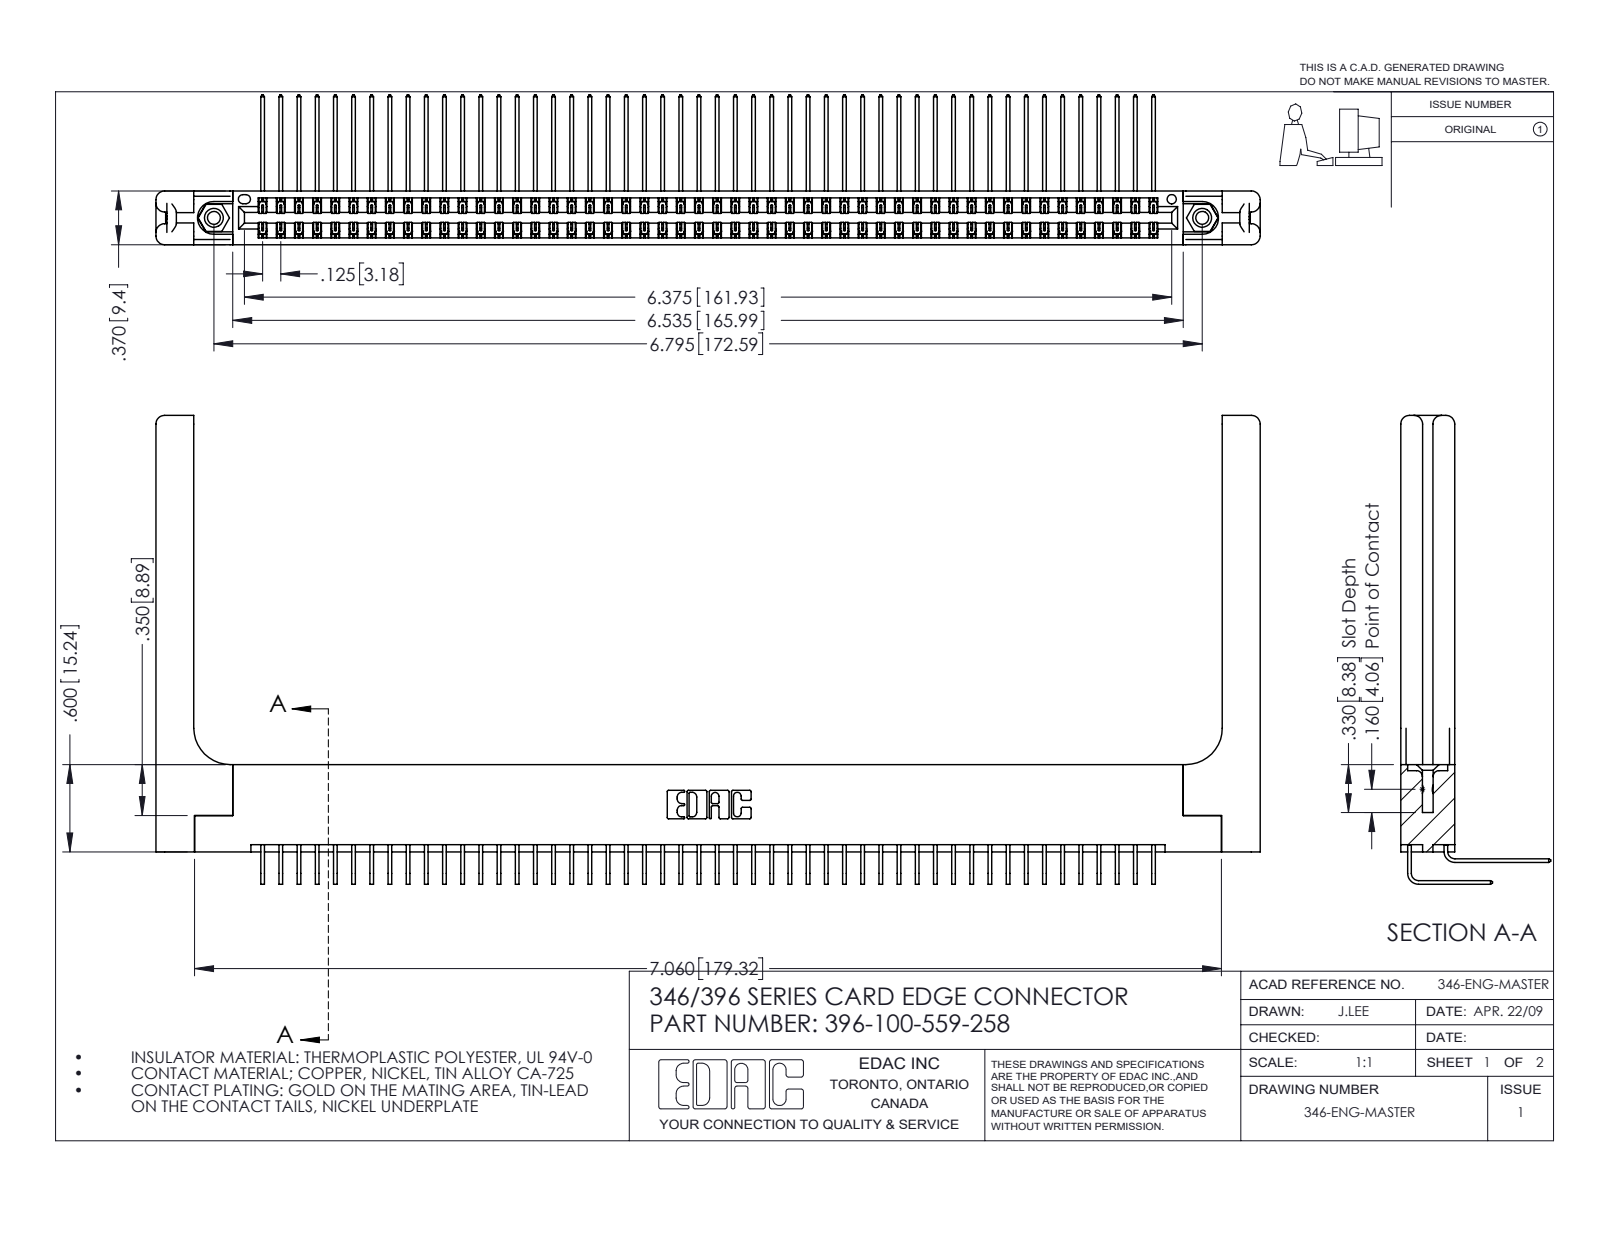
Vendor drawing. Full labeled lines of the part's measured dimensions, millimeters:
Part name (STEP PRODUCT): 345-292-001_558 559 Tail - 1; 345-250-001_345-250-001-102; 346 Part_Flush Mounting Lugs - 0.156 Dia-TH; 346-220-058_345-220-058 (+2 more)
STEP written by: SolidWorks 2016 (CONFIG_CONTROL_DESIGN)
Units: millimetres
Bodies: 105 solids, 5778 faces (3924 planar, 1794 cylindrical, 60 other)
Overall size (bounding box): 192.8 × 81.9 × 26.2
Volume: 26 940 mm³ · Surface area: 34 590 mm²
Round holes (diameter × count): ⌀2.3 ×2, ⌀3.2 ×2, ⌀4 ×2, ⌀1.6 ×1
Round bosses / shafts (diameter × count): ⌀3.9 ×2
Partial cylindrical surfaces — rounded edges, fillets, slot ends (radius × count): R0.2 ×150, R0.3 ×22, R1.5 ×16, R0.2 ×6, R0.8 ×6, R0.7 ×3, R0.4 ×2, R0.6 ×2
Main face-to-face distances: 1.2, 8.2, 9.4, 1.8, 0.6, 6.4, 3.8, 3.8, 7.6, 7
Hole centre spacings: 6.2, 167.3, 172.6
